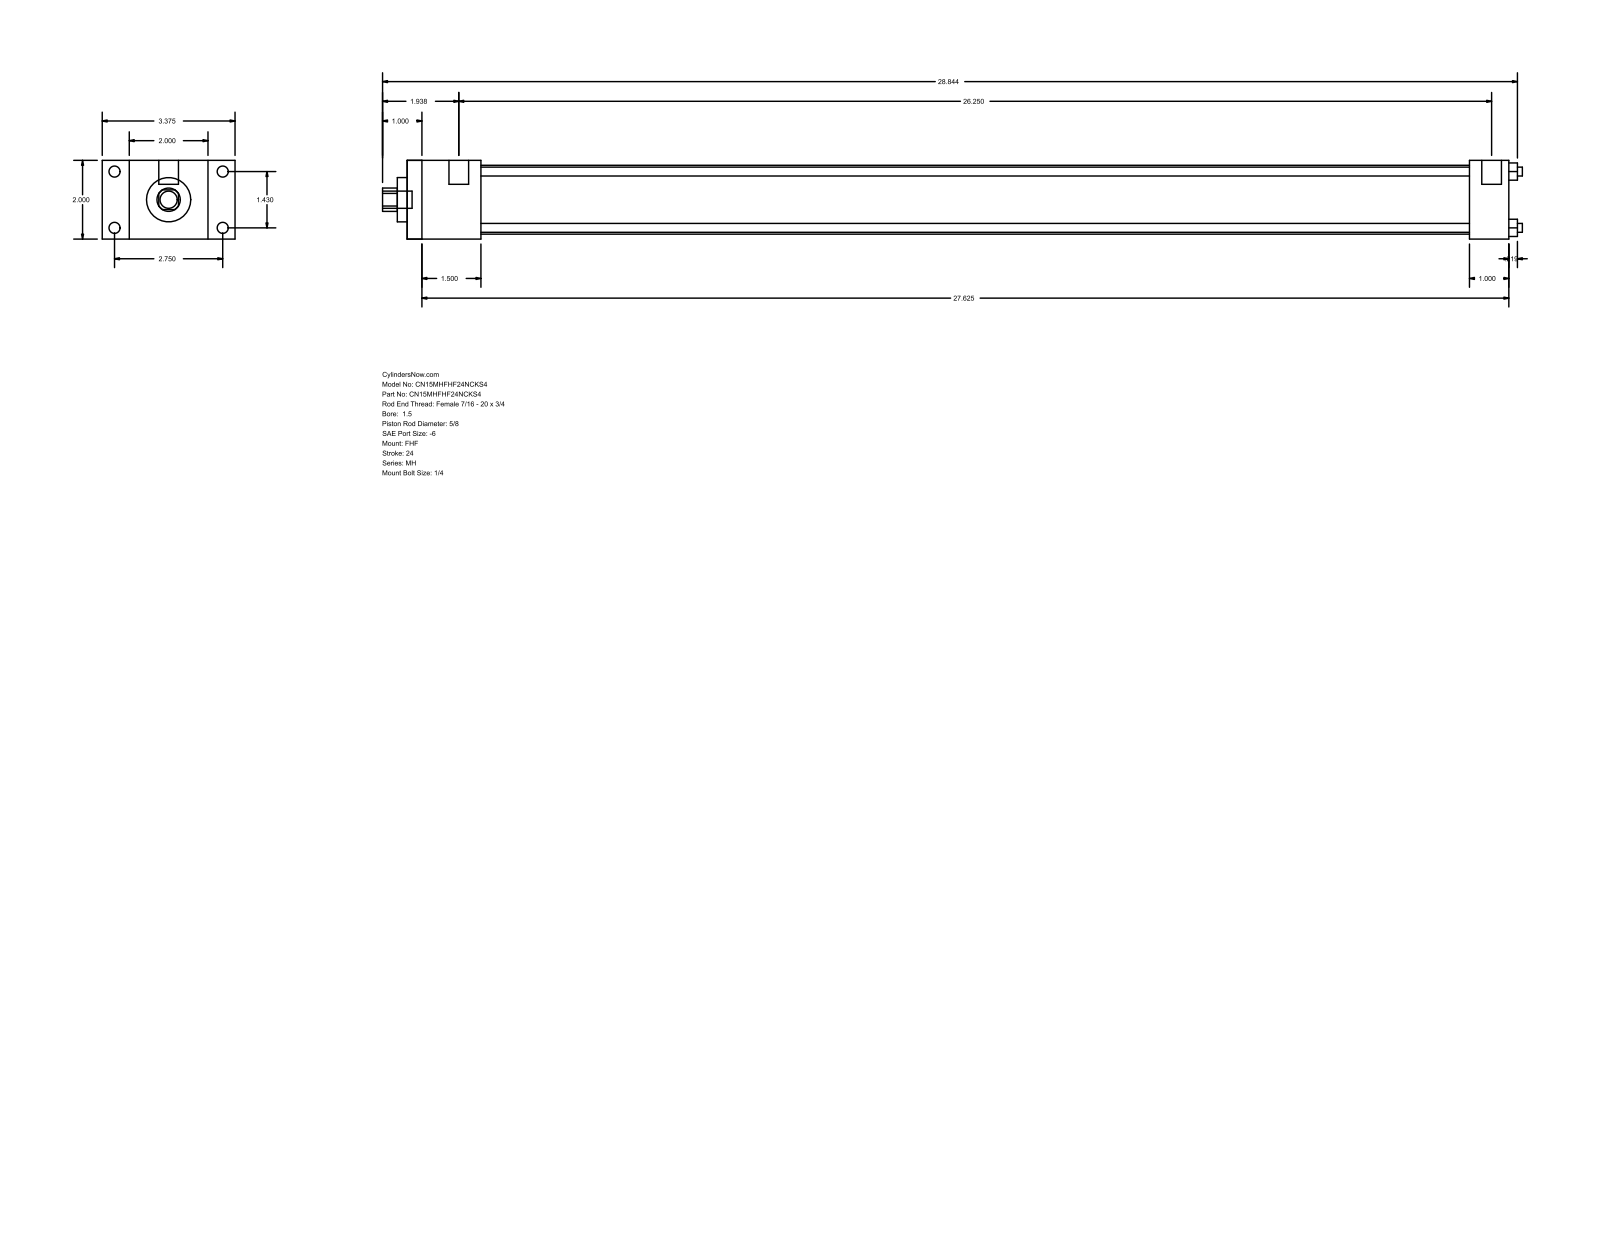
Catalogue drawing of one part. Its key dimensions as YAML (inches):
part_name: "MH_FHF__0150_0.625"
step_written_by: "GSSL Pune (CONFIG_CONTROL_DESIGN)"
units: inches
bodies: {solids: 0, faces: 88, planar: 60, cylindrical: 28, other: 0}
overall_size: [28.969, 3.375, 2]
round_holes:
  - {diameter: 0.225, count: 4}
  - {diameter: 0.625, count: 1}
  - {diameter: 1.125, count: 1}
  - {diameter: 1.75, count: 1}
round_bosses_or_shafts:
  - {diameter: 0.281, count: 4}
  - {diameter: 0.219, count: 4}
  - {diameter: 0.5, count: 2}
  - {diameter: 0.437, count: 1}
partial_cylinders:
  - {radius: 0.297, count: 1}
face_to_face_distances: [2, 0.687, 2.687, 1.875, 3.375, 28, 26.125, 27, 25.125, 1]
hole_center_spacings: [1.011, 1.43, 2.022]
